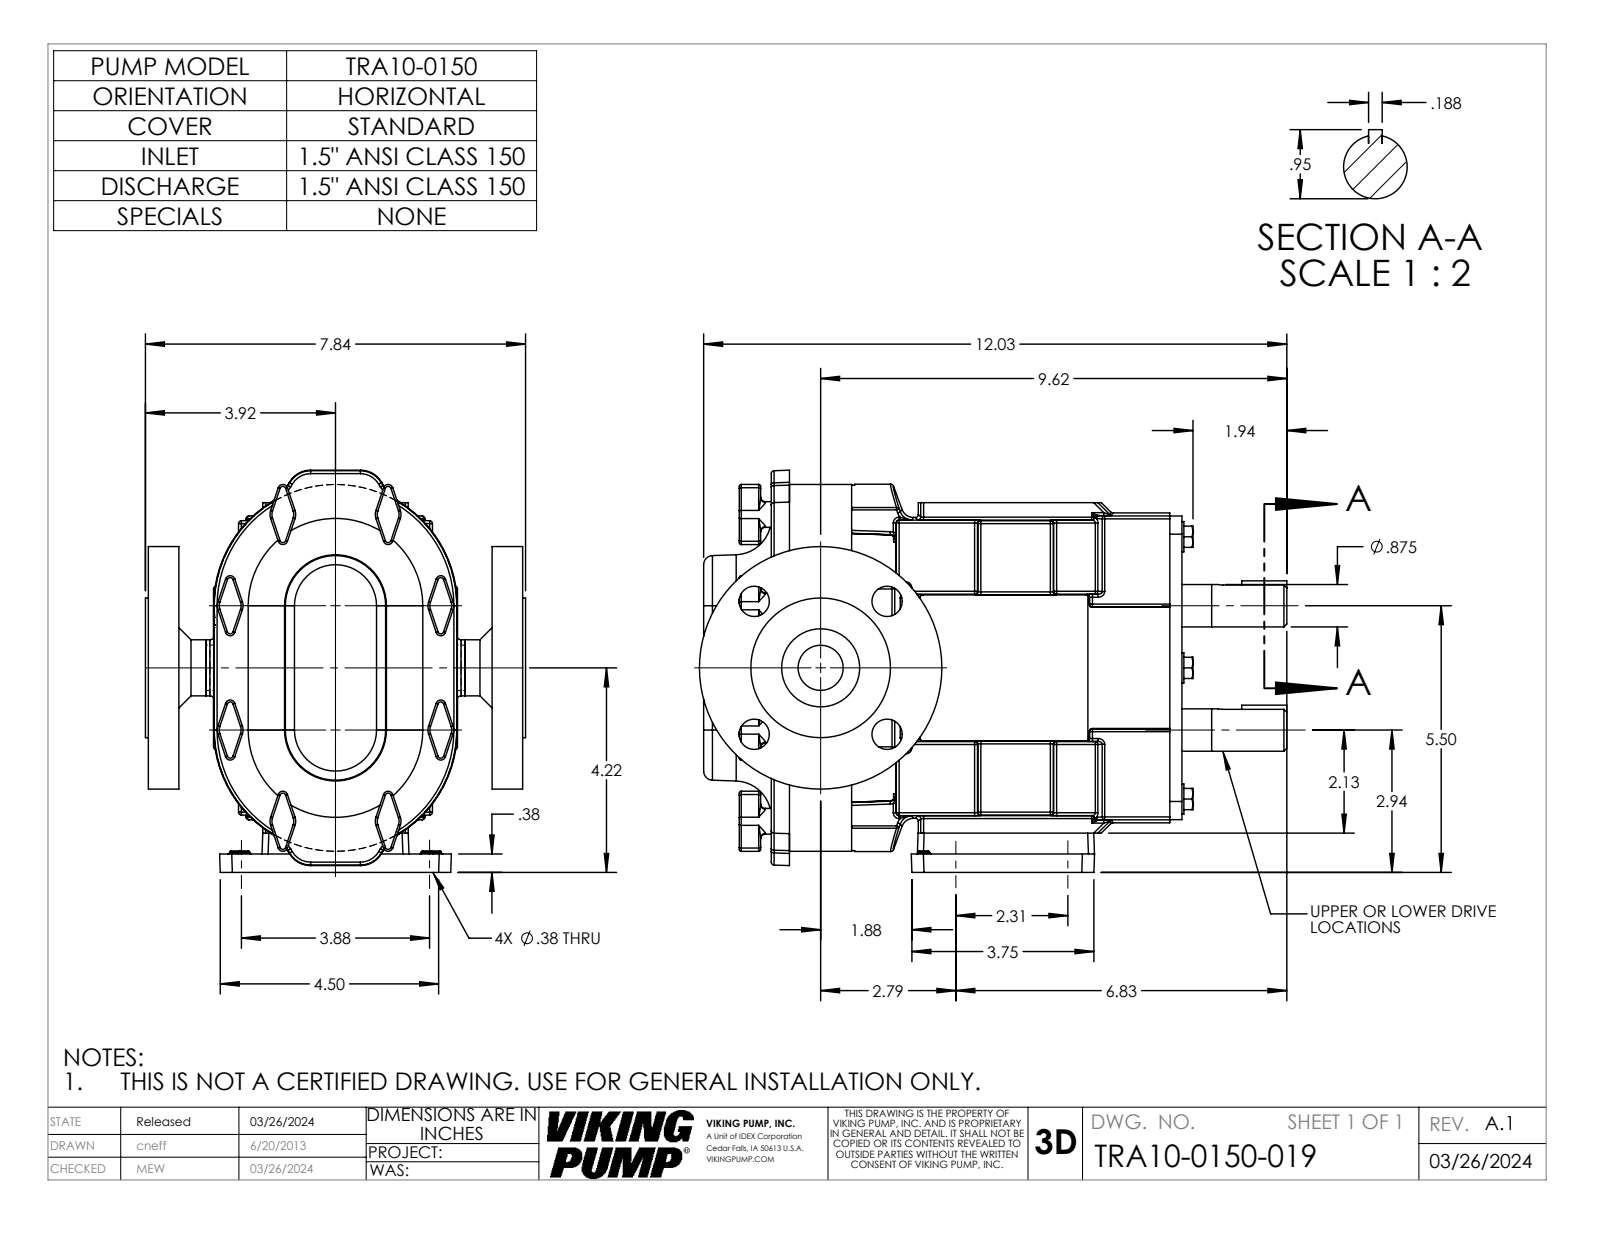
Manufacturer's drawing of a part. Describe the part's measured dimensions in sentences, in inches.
The part is named "TRA10-0150-COVER-STD; TRA10-0150-BODY; TRA10-0150-019; 0150FLG150-15 (+1 more)". Its 3-D file was written by "SolidWorks 2022 (AUTOMOTIVE_DESIGN)". It is 5 solids with 1203 faces: 321 planar, 469 cylindrical and 413 other. Overall it measures 12.115 by 8.292 by 7.84 inches. Its volume is 255.5 cubic inches and its surface area 577.1 square inches. Round holes: 4 of diameter 0.375, 4 of diameter 0.625, 1 of diameter 0.931, 1 of diameter 0.937, 1 of diameter 1.61. Round bosses or shafts: 8 of diameter 0.53, 6 of diameter 0.625, 2 of diameter 0.874, 1 of diameter 5, 1 of diameter 2.88, 1 of diameter 1.156. Partial cylindrical surfaces (rounded edges, fillets, slot ends): 189 of radius 0.06, 64 of radius 0.04, 20 of radius 0.125, 16 of radius 0.03, 16 of radius 0.1, 14 of radius 0.25, 4 of radius 0.375, 4 of radius 0.5. The main face-to-face distances are 1.282, 0.63, 7.09, 1.735, 5.985, 1.105, 5.355, 8.094, 6.813, 6.46. The hole center spacings are 1.937, 2.74, 2.31, 3.875, 3.88, 4.516.
